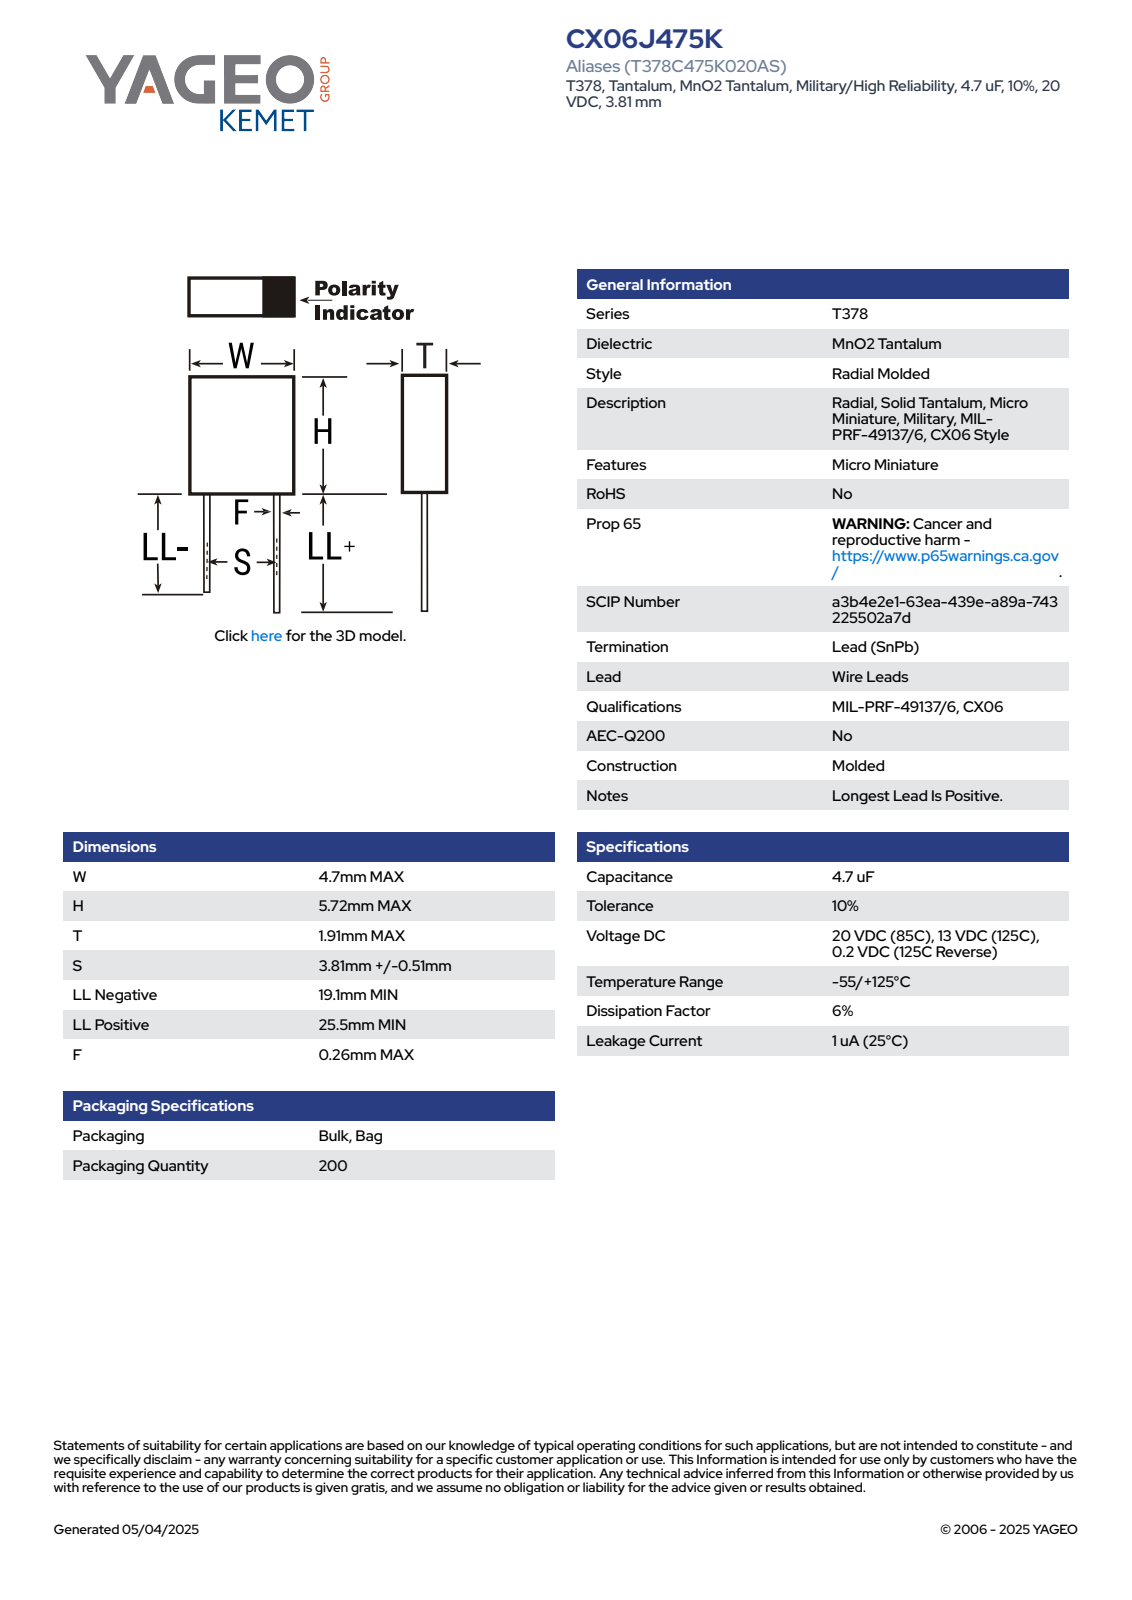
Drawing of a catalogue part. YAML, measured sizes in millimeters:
part_name: "CTRM_T378_W4.7H5.72T1.91S3.81LL44.46F0.44"
step_written_by: "SolidWorks 2014 (AUTOMOTIVE_DESIGN)"
units: millimeters
bodies: {solids: 4, faces: 71, planar: 67, cylindrical: 4, other: 0}
overall_size: [50.18, 4.7, 1.92]
volume: 64
surface_area: 212
round_bosses_or_shafts:
  - {diameter: 0.44, count: 2}
face_to_face_distances: [1.91, 4.7, 5.71, 5.72, 1.92, 38.11, 43.82, 43.83, 6.35, 44.46]
